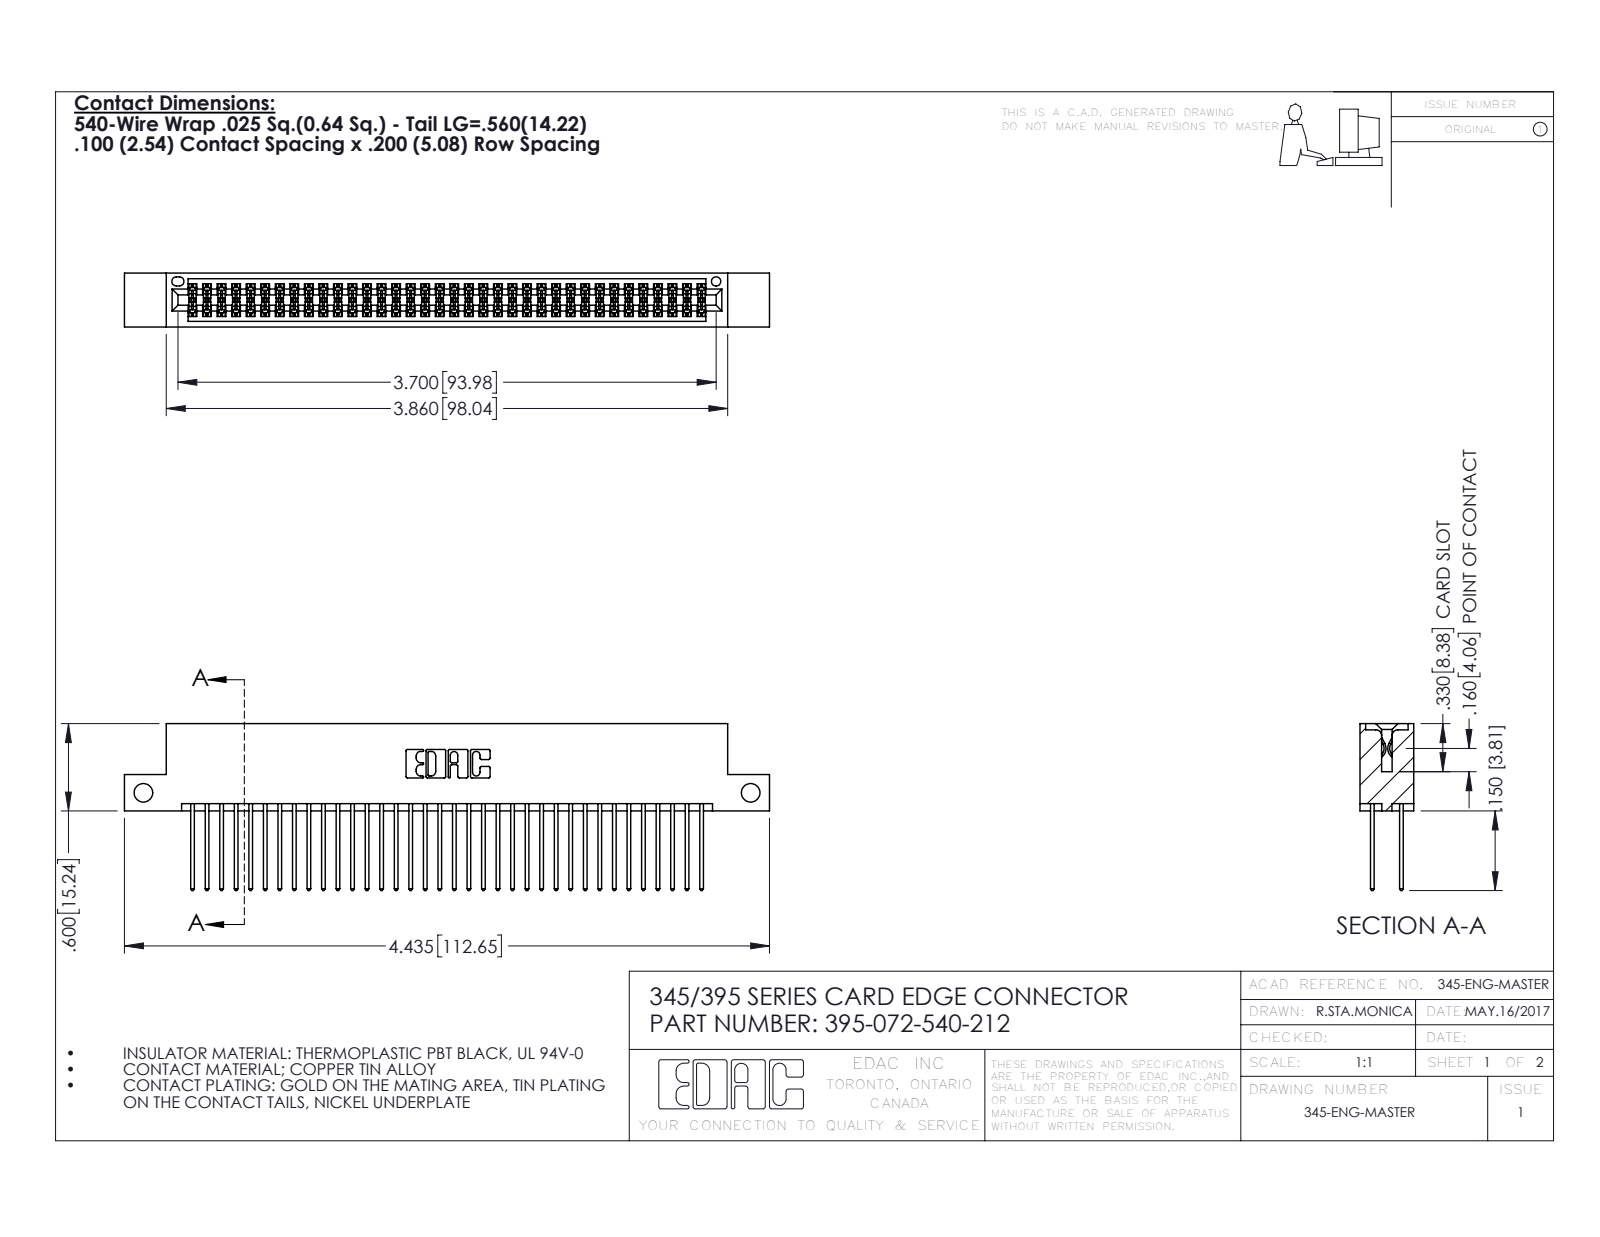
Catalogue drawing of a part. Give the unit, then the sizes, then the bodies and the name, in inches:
Units: inches
Overall size (bounding box): 4.435 × 1.147 × 0.37
Round holes (diameter × count): ⌀0.128 ×2, ⌀0.064 ×1
Partial cylindrical surfaces — rounded edges, fillets, slot ends (radius × count): R0.006 ×108, R0.01 ×72, R0.01 ×22, R0.007 ×6, R0.031 ×6, R0.026 ×3, R0.014 ×2, R0.019 ×2
Main face-to-face distances: 0.298, 0.072, 0.2, 0.098, 0.272, 0.025, 0.37, 0.225, 0.175, 0.149
Hole centre spacings: 4.175
Volume: 0.676 in³ · Surface area: 26.94 in²
Bodies: 73 solids, 3726 faces (2456 planar, 1270 cylindrical, 0 other)
Part name (STEP PRODUCT): 345 Part_Flush Mounting Lugs - Side Mount; 395-072-540-212; 345-292-001_345-293-140
STEP written by: SolidWorks 2016 (CONFIG_CONTROL_DESIGN)
